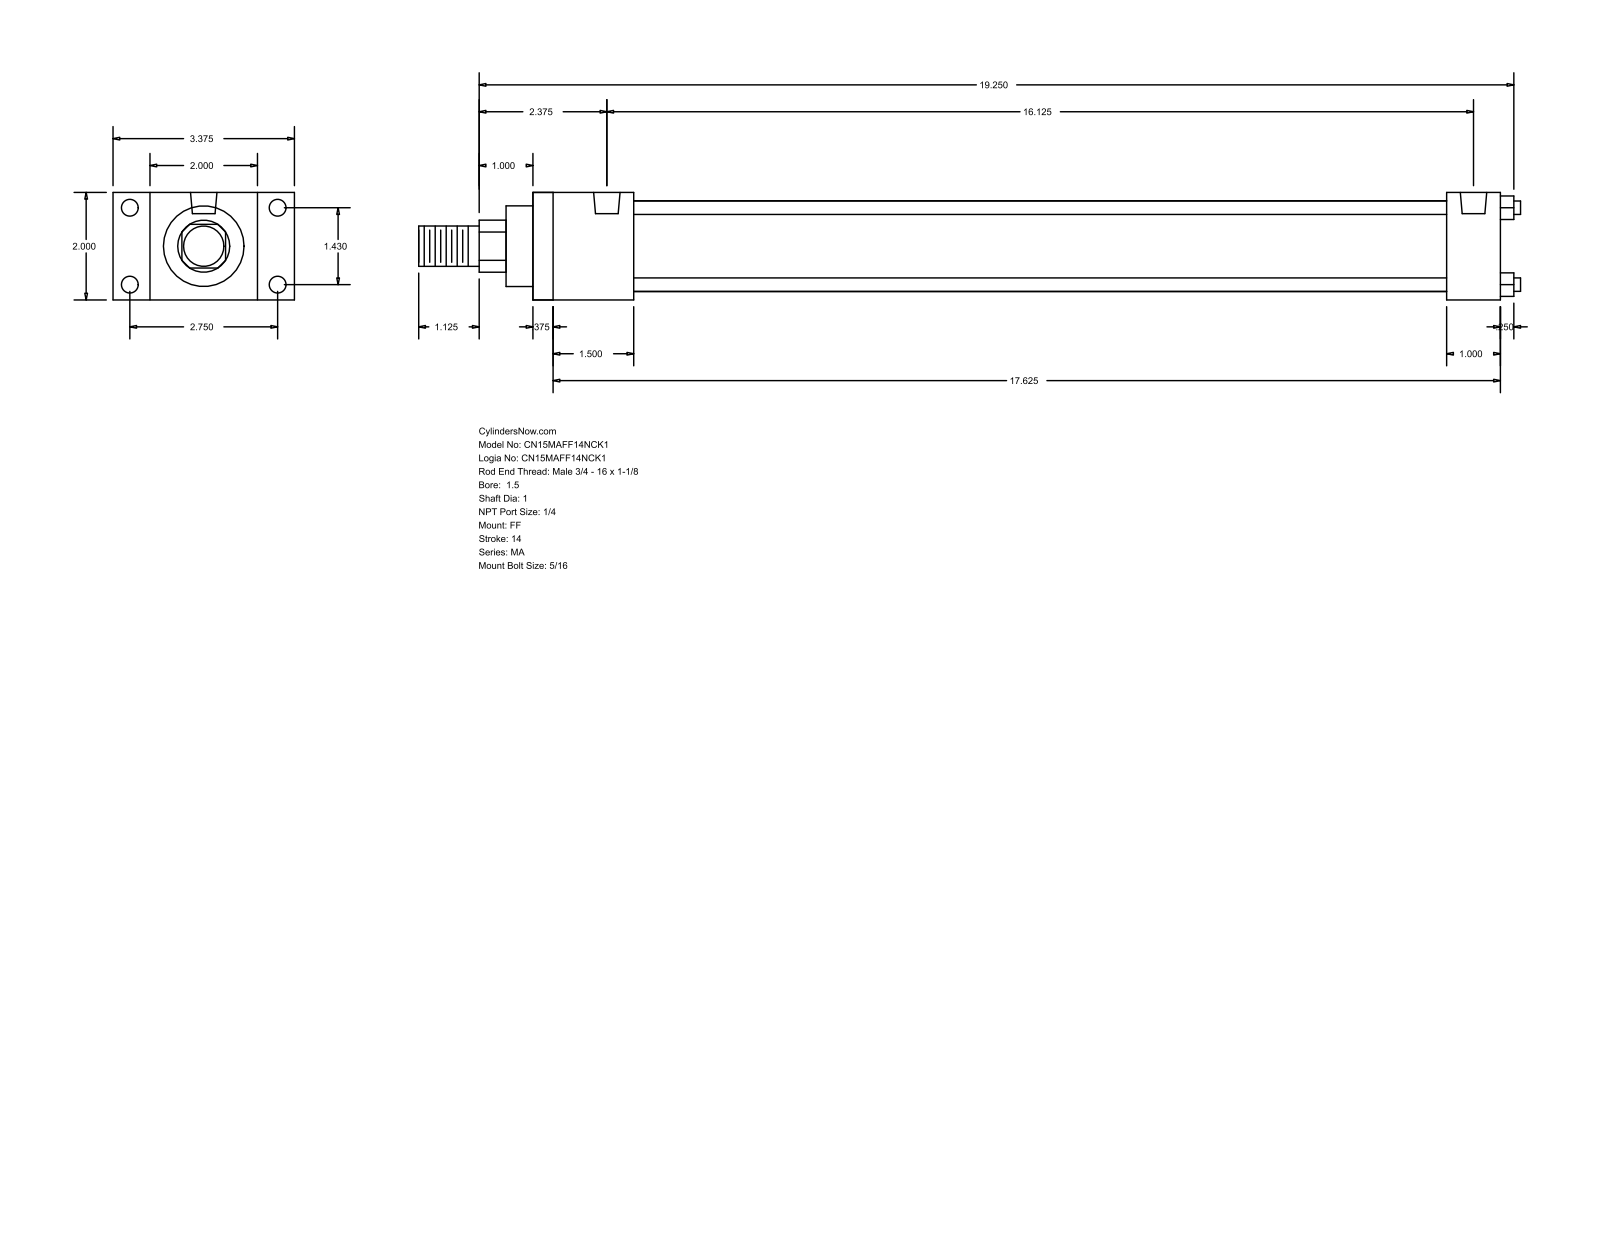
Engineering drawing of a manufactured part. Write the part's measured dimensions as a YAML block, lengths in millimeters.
part_name: "MA_FF__0150_1"
step_written_by: "GSSL Pune (CONFIG_CONTROL_DESIGN)"
units: millimeters
bodies: {solids: 0, faces: 92, planar: 64, cylindrical: 28, other: 0}
overall_size: [520.7, 85.72, 50.8]
round_holes:
  - {diameter: 7.94, count: 8}
  - {diameter: 12.49, count: 2}
round_bosses_or_shafts:
  - {diameter: 6.35, count: 4}
  - {diameter: 42.93, count: 1}
  - {diameter: 38.1, count: 1}
  - {diameter: 25.4, count: 1}
  - {diameter: 19.05, count: 1}
partial_cylinders:
  - {radius: 12.29, count: 1}
face_to_face_distances: [50.8, 457.2, 9.52, 447.68, 25.4, 47.63, 431.8, 38.11, 422.28, 384.17]
hole_center_spacings: [36.32, 69.84, 78.72, 409.57]
